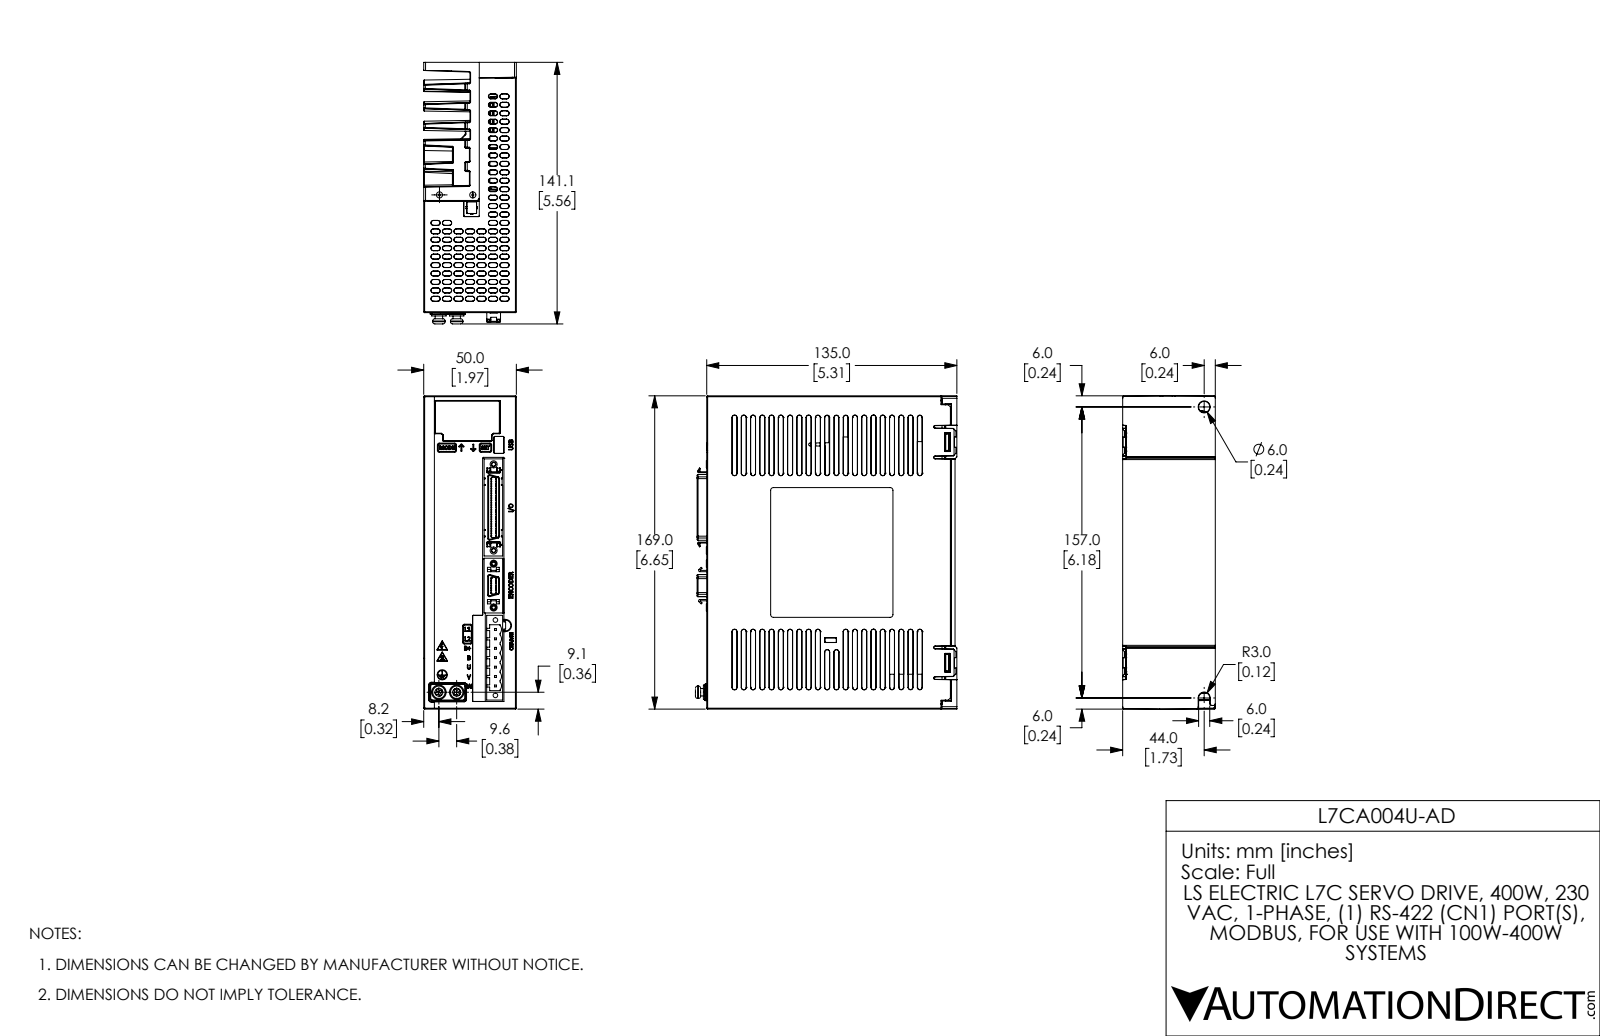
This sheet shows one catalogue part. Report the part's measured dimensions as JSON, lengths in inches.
{"part_name": "L7C 200V (100W,200W,400W) Delete 2 screw washers for faces 1-17 long Conn other faces 1 ext1 228fcs redonly1B2rob r1ro COMPLETE 3", "step_written_by": "SolidWorks 2017 (AUTOMOTIVE_DESIGN)", "units": "inches", "bodies": {"solids": 4, "faces": 4661, "planar": 2309, "cylindrical": 915, "other": 1437}, "overall_size": [6.667, 5.555, 1.969], "volume_in3": 51.35, "surface_area_in2": 277.4, "round_holes": [[0.098, 12], [0.079, 2], [0.102, 2], [0.13, 2]], "round_bosses_or_shafts": [[0.15, 4], [0.307, 2], [0.264, 2], [0.157, 2]], "partial_cylinders_radius": [[0.012, 259], [0.02, 153], [0.039, 59], [0.016, 31], [0.008, 28], [0.01, 18], [0.13, 7], [0.005, 6]], "face_to_face_distances": [0.413, 1.969, 0.228, 1.74, 1.677, 0.063, 0.291, 0.826, 5.276, 0.02], "hole_center_spacings": [1.26, 1.781, 0.268, 0.28, 0.594, 0.597, 0.665, 0.668]}
